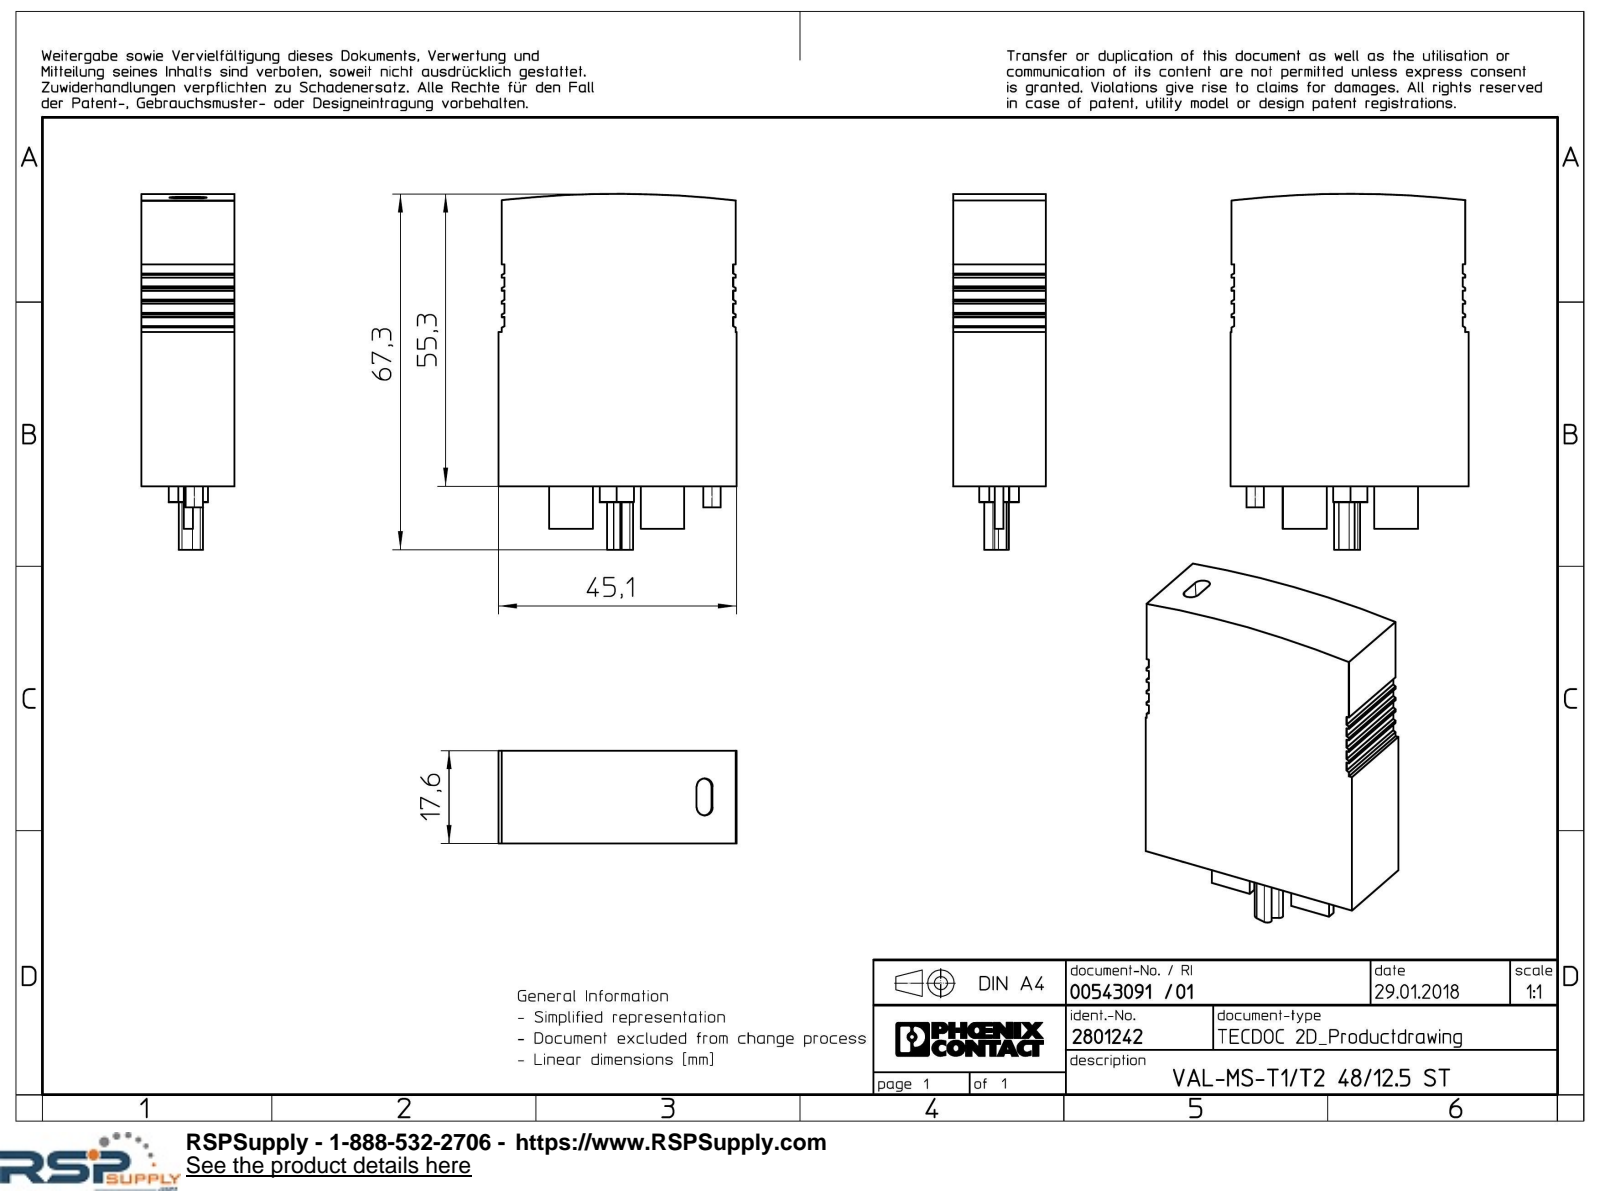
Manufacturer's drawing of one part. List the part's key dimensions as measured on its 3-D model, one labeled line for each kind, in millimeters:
Part name (STEP PRODUCT): VAL_MS_T1_T2...12.5_ST-select
STEP written by: Creo Elements/Direct Modeling 20.1A 29-Sep-2018 (C) Parametric Technology GmbH (AUTOMOTIVE_DESIGN)
Units: millimetres
Bodies: 1 solid, 86 faces (75 planar, 9 cylindrical, 2 other)
Overall size (bounding box): 67.3 × 45.1 × 17.6
Volume: 43 492 mm³ · Surface area: 9 163 mm²
Round bosses / shafts (diameter × count): ⌀3.3 ×1
Partial cylindrical surfaces — rounded edges, fillets, slot ends (radius × count): R0.82 ×3, R0.19 ×2, R1.22 ×1, R200 ×1
Main face-to-face distances: 17.6, 45.1, 0.65, 44.45, 0.5, 43.8, 44.95, 44.3, 1.15, 43.95
